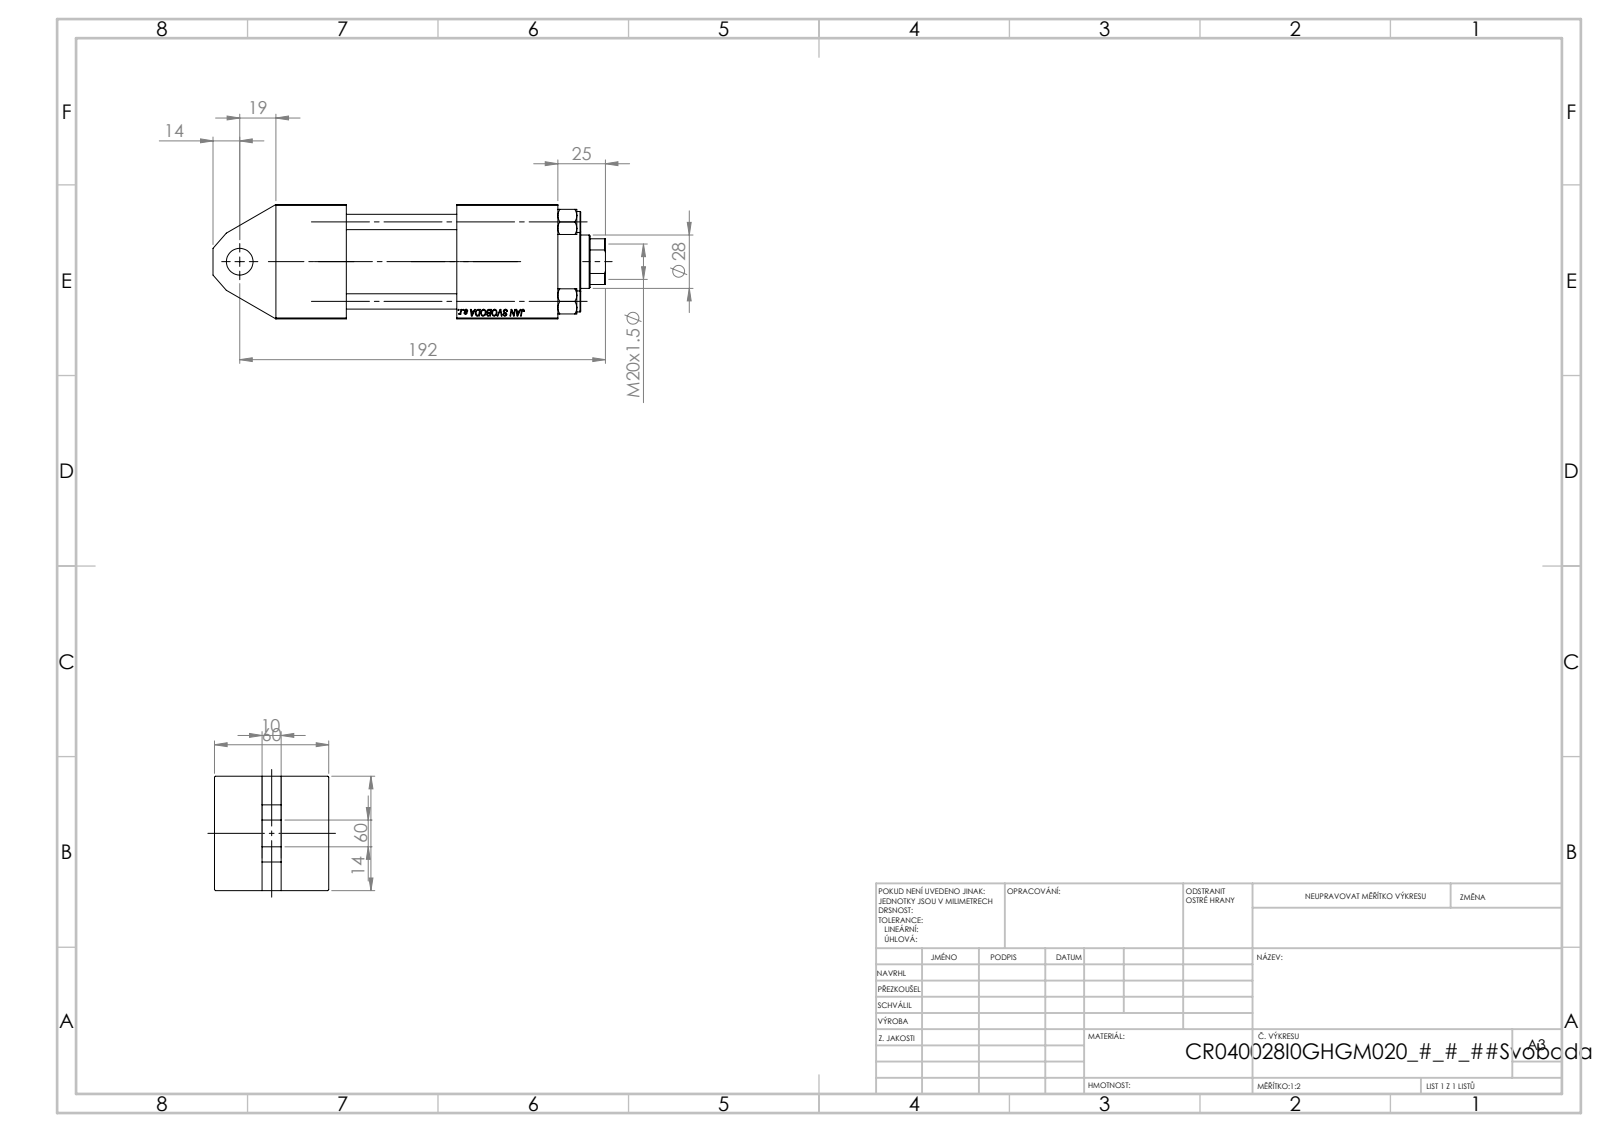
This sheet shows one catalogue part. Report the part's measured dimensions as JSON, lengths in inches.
{"part_name": "V215CR_TYCINKA_I; V215CR_I_Body; V215_VC_A; NUT_M5_I (+1 more)", "step_written_by": "SolidWorks 2019 (CONFIG_CONTROL_DESIGN)", "units": "inches", "bodies": {"solids": 11, "faces": 1079, "planar": 502, "cylindrical": 81, "other": 496}, "overall_size": [8.11, 2.362, 2.362], "volume_in3": 26.84, "surface_area_in2": 179.3, "round_holes": [[0.315, 4], [0.276, 2], [0.656, 2], [0.945, 2], [0.551, 1], [0.728, 1], [1.102, 1], [1.22, 1], [1.575, 1], [1.772, 1]], "round_bosses_or_shafts": [[0.433, 4], [1.811, 1], [1.654, 1]], "partial_cylinders_radius": [[0.531, 1]], "face_to_face_distances": [2.362, 1.457, 0.984, 2.087, 1.378, 2.283, 3.74, 5.827, 4.37, 4.697], "hole_center_spacings": [1.161, 1.642, 2.322, 1.476, 3.642, 5.118]}
